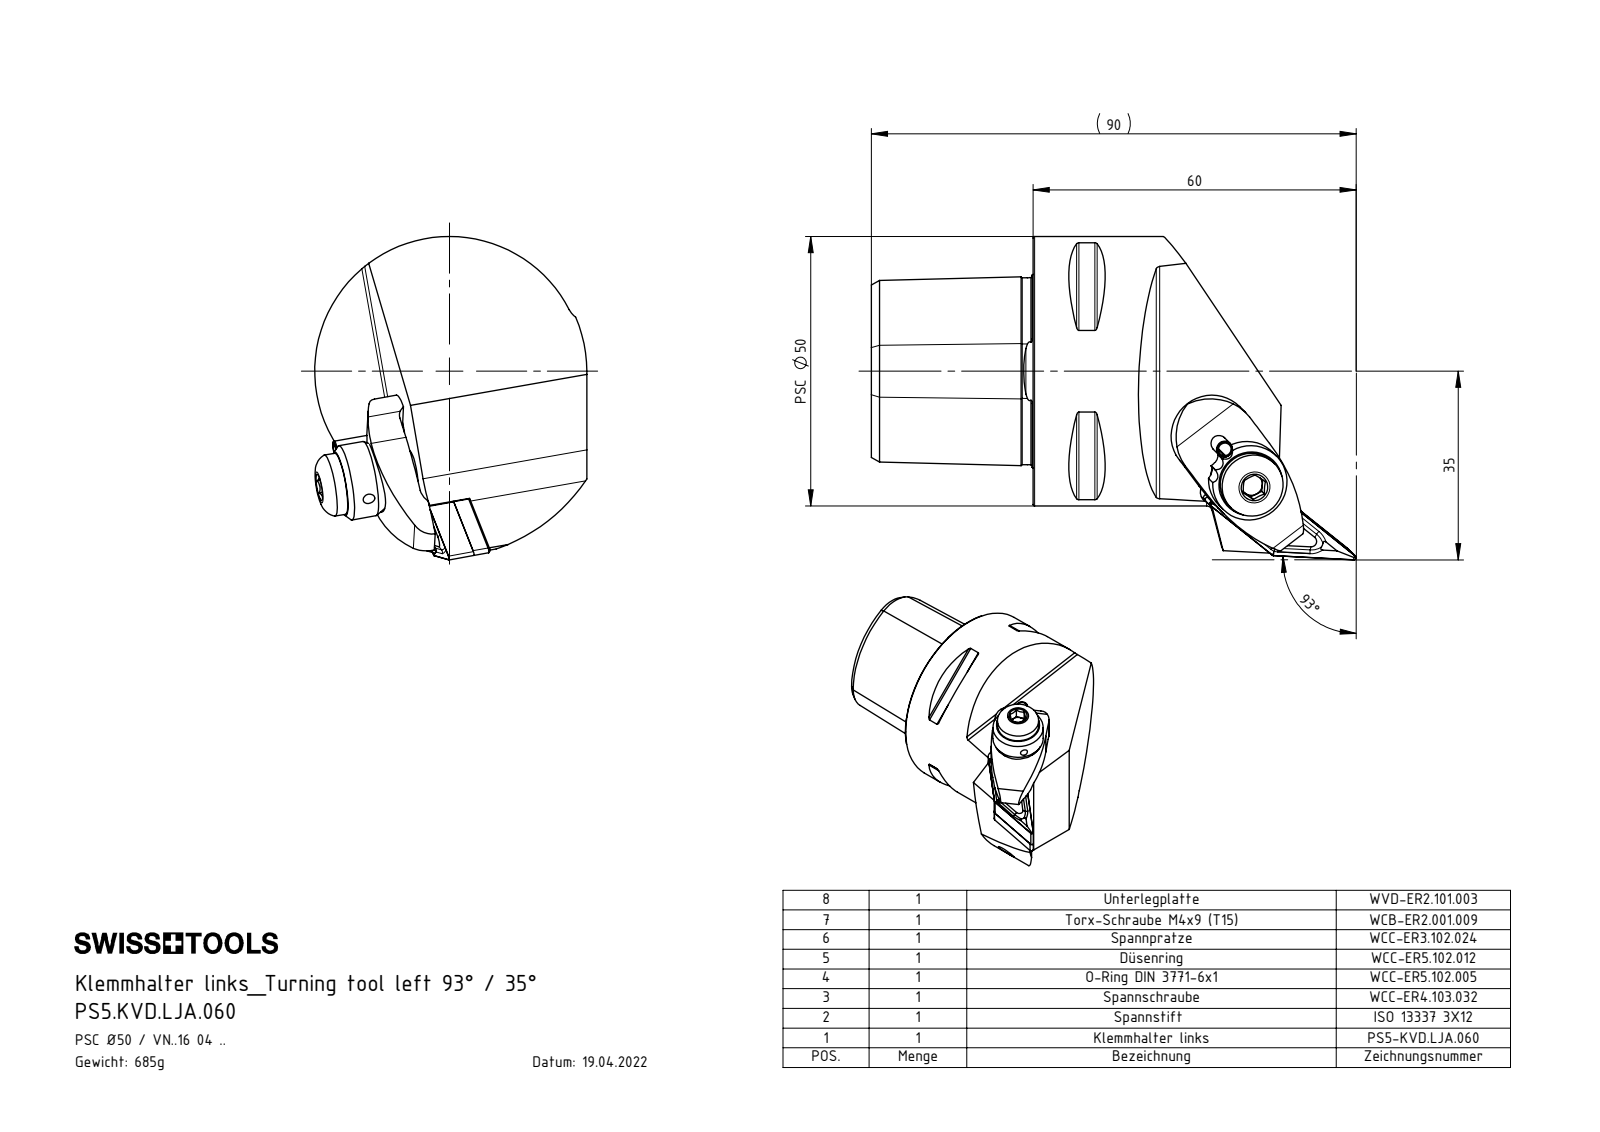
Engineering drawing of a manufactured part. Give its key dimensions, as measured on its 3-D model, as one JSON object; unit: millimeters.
{"part_name": "WCC-ER3.102.024_C; WVD-ER2.101.003_A; PS5-KVD.LJA.060_A; WCB-ER2.001.009_A (+7 more)", "step_written_by": "SolidWorks 2017 (AUTOMOTIVE_DESIGN)", "units": "millimeters", "bodies": {"solids": 11, "faces": 431, "planar": 100, "cylindrical": 134, "other": 197}, "overall_size": [90, 60, 50.5], "volume_mm3": 86733, "surface_area_mm2": 23192, "round_holes": [[2, 3], [4, 2], [5, 2], [7, 2], [2.4, 1], [3, 1], [3.3, 1], [3.8, 1], [4.2, 1], [4.95, 1], [6.1, 1], [6.2, 1]], "round_bosses_or_shafts": [[4, 2], [3, 2], [50, 1], [14, 1], [11.5, 1], [6.8, 1], [6, 1], [5.25, 1]], "partial_cylinders_radius": [[0.5, 10], [0.34, 6], [0.59, 6], [0.4, 4], [1.5, 3], [2, 2], [3, 2], [4, 2]], "face_to_face_distances": [30, 9.12, 7.64, 3.18, 4.46, 9.53, 1.3, 8.94, 5.76, 0.41], "hole_center_spacings": [22.32, 8.02, 14.12, 14.3, 8.2, 8.21, 22.33, 26]}
